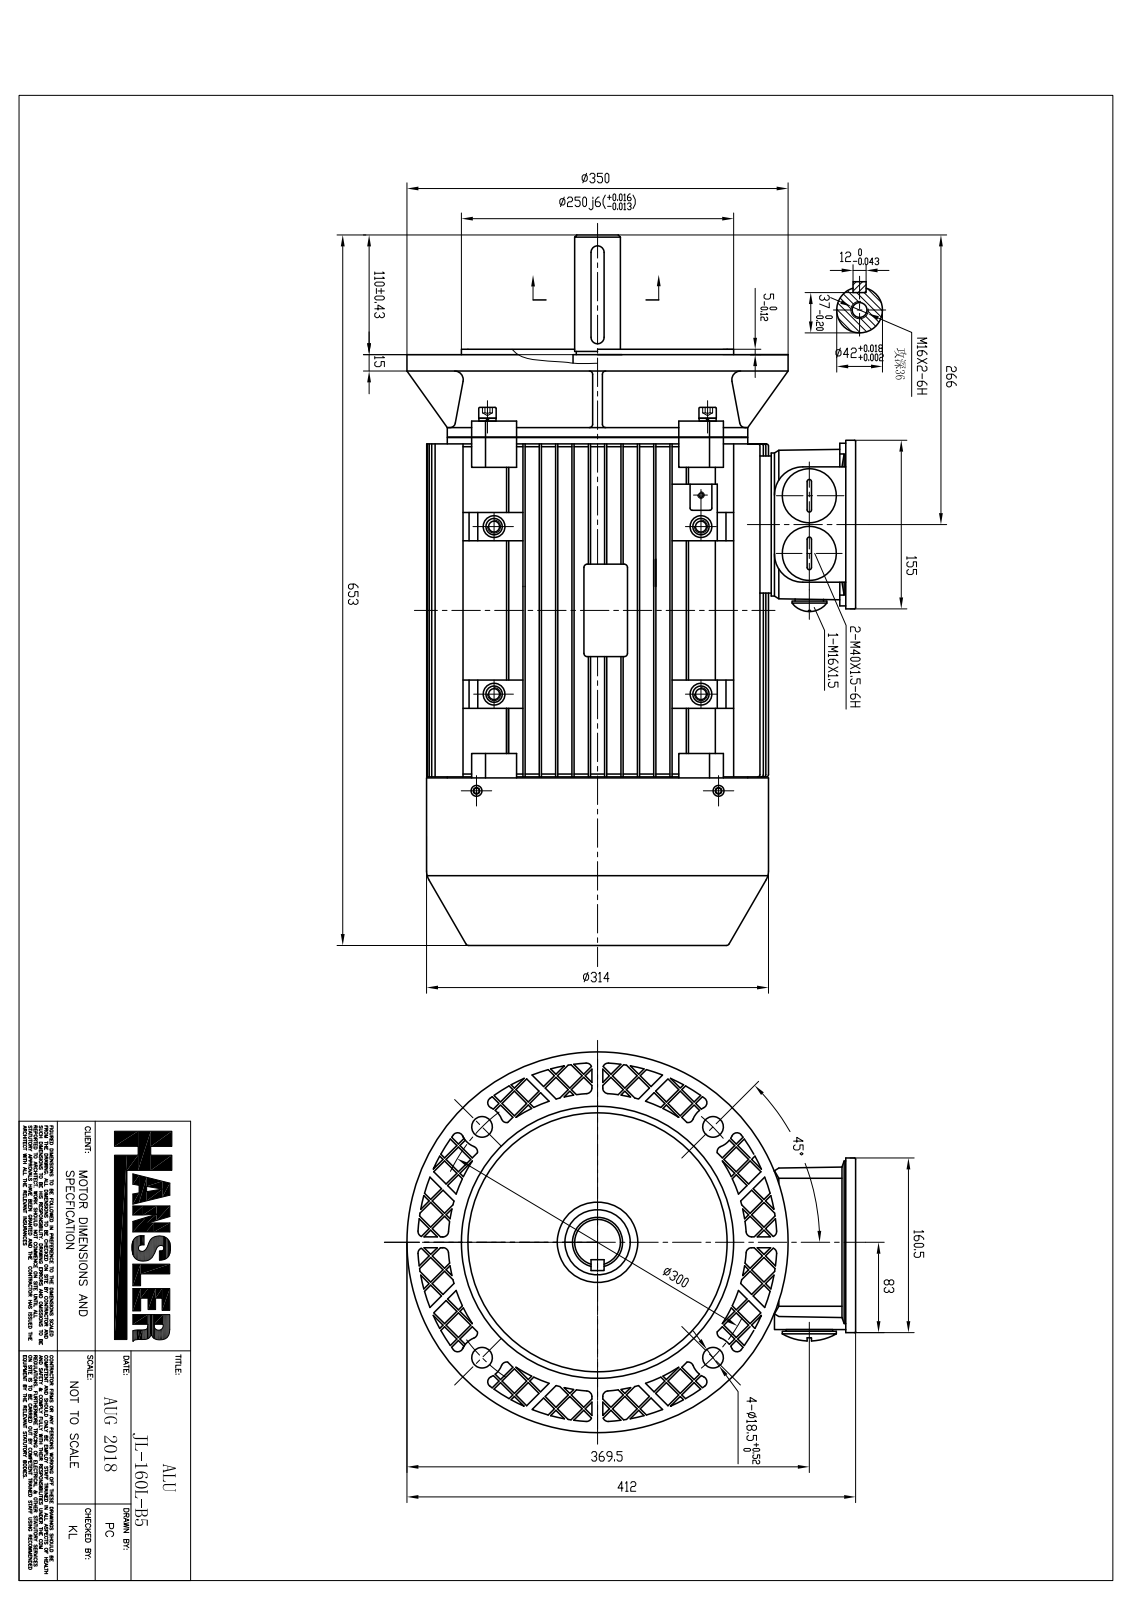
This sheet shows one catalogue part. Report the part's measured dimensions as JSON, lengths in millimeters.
{"part_name": "JL-160L-B5", "step_written_by": "SIEMENS PLM Software NX 12.0 (AP203_CONFIGURATION_CONTROLLED_3D_DESIGN_OF_MECHANICAL_PARTS_AND_ASSEMBLIES_MIM_LF)", "units": "millimeters", "bodies": {"solids": 57, "faces": 8087, "planar": 3770, "cylindrical": 1966, "other": 2351}, "overall_size": [650.92, 417.7, 350], "volume_mm3": 7331000, "surface_area_mm2": 2774000, "round_holes": [[5, 28], [4.12, 12], [8.39, 8], [9.1, 8], [10, 8], [12, 8], [21, 8], [5.25, 5], [5.3, 5], [8, 5], [4.2, 4], [5.48, 4]], "round_bosses_or_shafts": [[8, 10], [5.38, 9], [15, 8], [12.59, 8], [7.19, 8], [10, 5], [7.85, 5], [4.48, 5]], "partial_cylinders_radius": [[1.2, 302], [1, 169], [2, 68], [4, 40], [1.37, 37], [3.42, 25], [3, 20], [0.81, 18]], "face_to_face_distances": [15, 30, 45, 2, 60, 75, 13, 17, 90, 28], "hole_center_spacings": [202.36, 207.25, 14.64, 202.24, 207.24, 95.35, 134, 202.23]}
